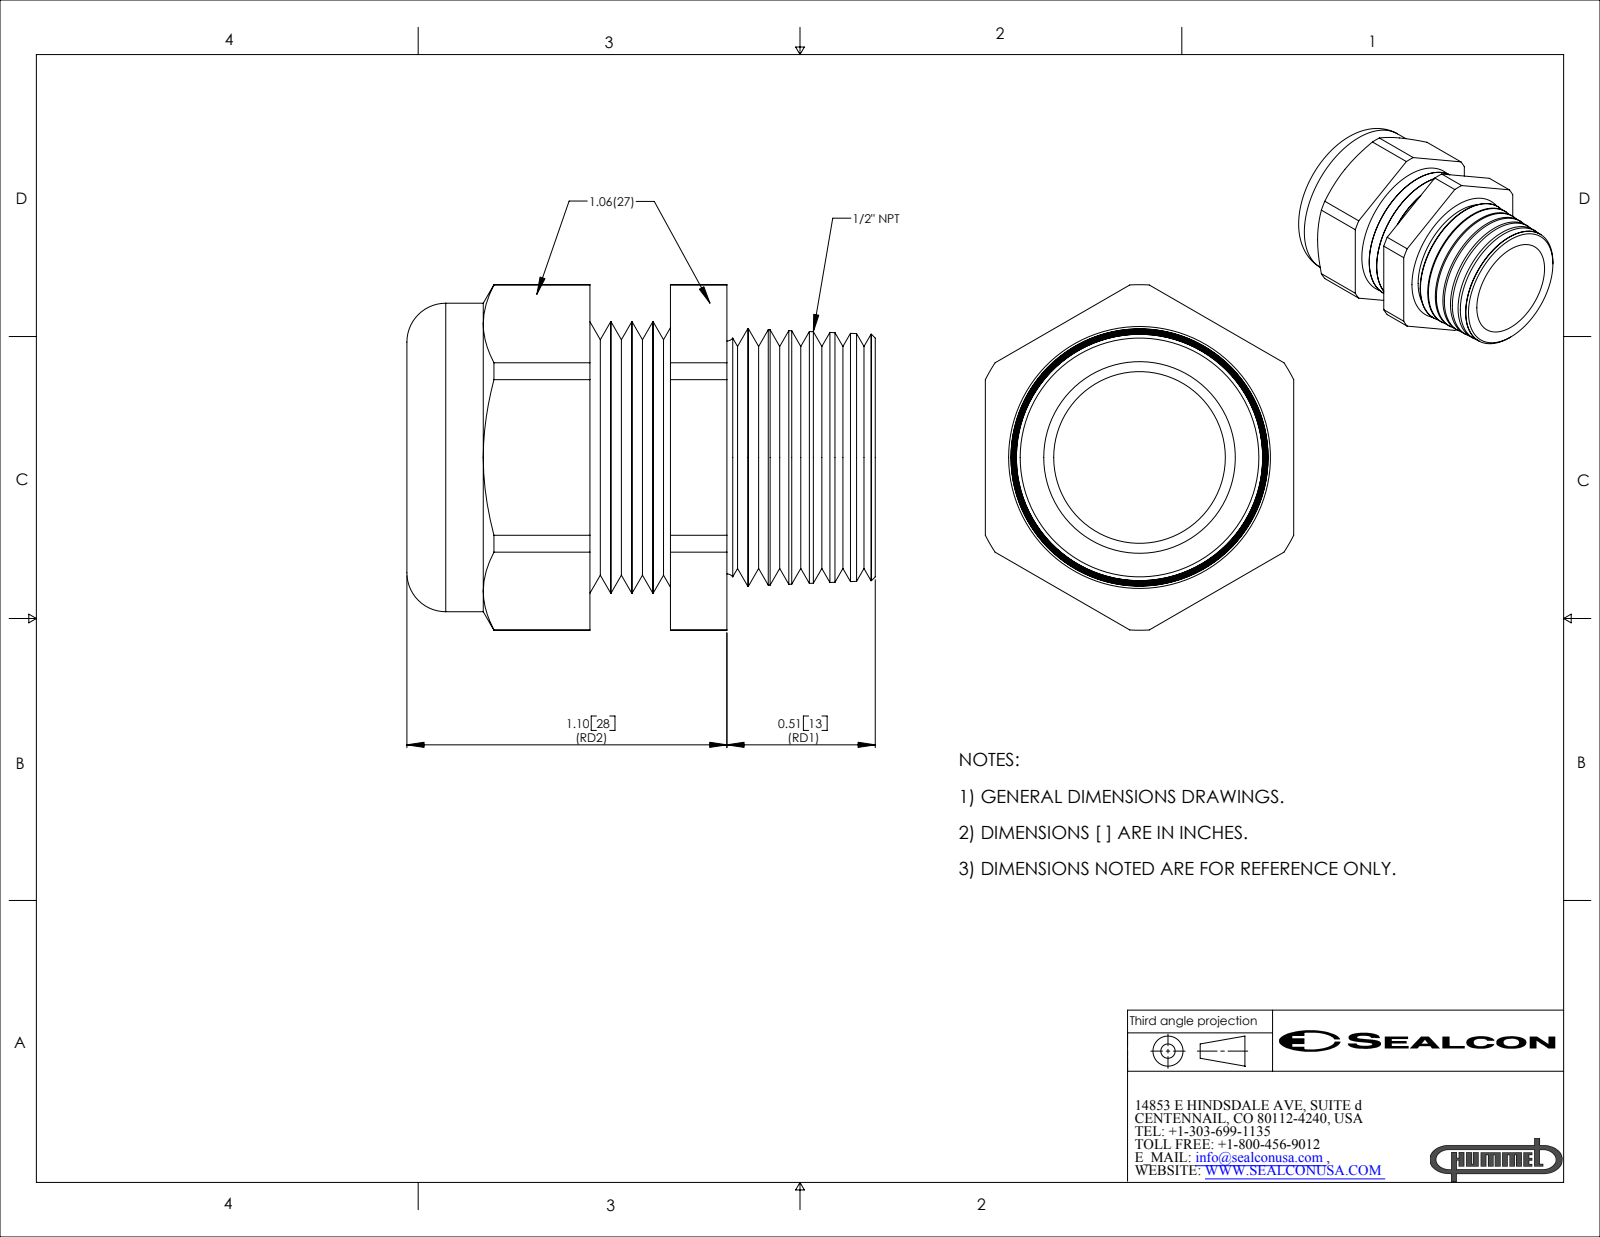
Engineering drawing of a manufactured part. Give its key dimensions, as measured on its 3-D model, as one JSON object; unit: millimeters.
{"part_name": "CD16NA-BK", "step_written_by": "SolidWorks 2007 (CONFIG_CONTROL_DESIGN)", "units": "millimeters", "bodies": {"solids": 2, "faces": 126, "planar": 20, "cylindrical": 30, "other": 76}, "overall_size": [40.9, 30.1, 26.9], "volume_mm3": 11800, "surface_area_mm2": 8535, "round_holes": [[15, 1], [19.2, 1]], "round_bosses_or_shafts": [[26.9, 1], [23.7, 1]], "partial_cylinders_radius": [[15.1, 1]], "face_to_face_distances": [26.9, 21.3, 9.3, 12, 16.3, 7, 4.9, 34.2, 24.9, 17.9]}
